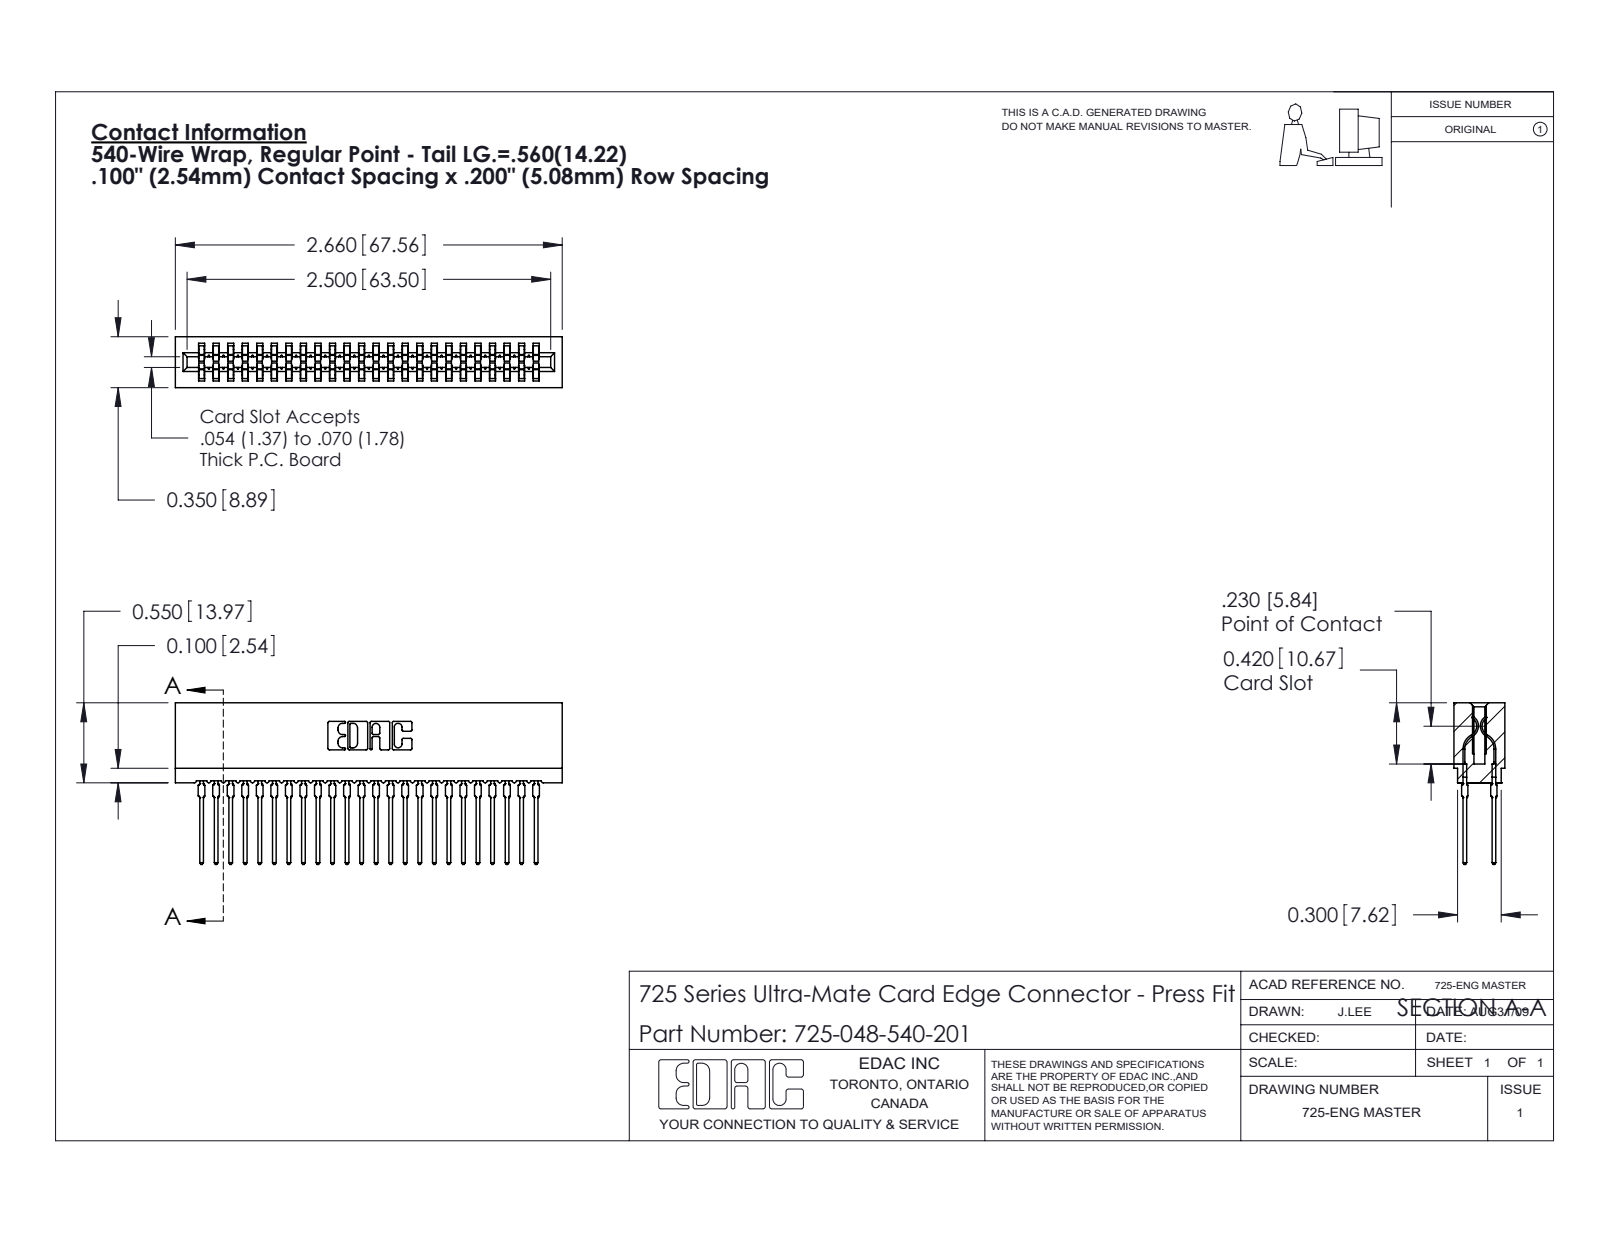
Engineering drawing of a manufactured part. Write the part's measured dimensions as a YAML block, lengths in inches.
part_name: "745-292-001_540; 725-048-540-201; 725 Part_Insulator Option - 01"
step_written_by: "SolidWorks 2020 (CONFIG_CONTROL_DESIGN)"
units: inches
bodies: {solids: 49, faces: 4391, planar: 2263, cylindrical: 880, other: 1248}
overall_size: [2.66, 1.111, 0.35]
volume: 0.341
surface_area: 18.57
partial_cylinders:
  - {radius: 0.021, count: 96}
  - {radius: 0.015, count: 48}
  - {radius: 0.01, count: 22}
  - {radius: 0.005, count: 8}
  - {radius: 0.011, count: 8}
  - {radius: 0.007, count: 6}
  - {radius: 0.031, count: 6}
  - {radius: 0.026, count: 3}
face_to_face_distances: [0.2, 0.1, 0.063, 0.287, 0.3, 0.4, 0.5, 0.35, 0.6, 0.7]
